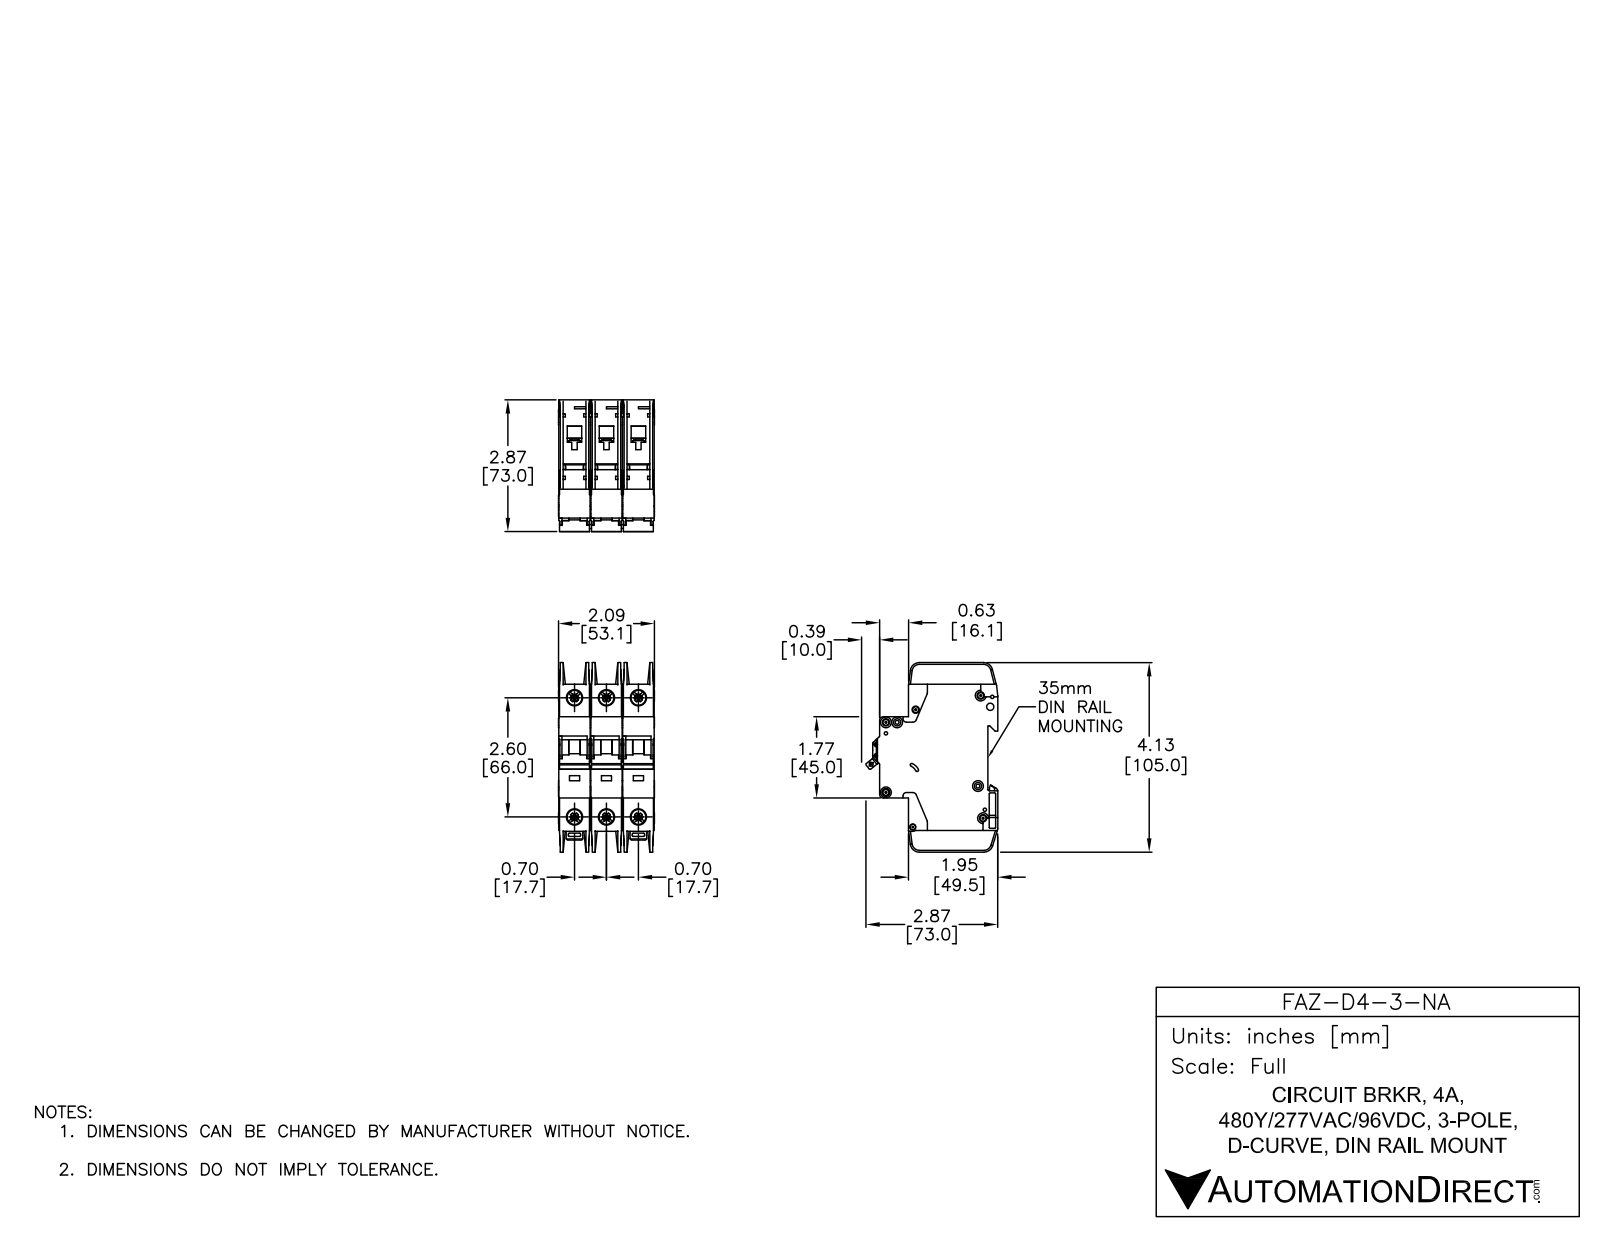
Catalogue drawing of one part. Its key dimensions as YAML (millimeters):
part_name: "FAZ-D4-3-NA"
step_written_by: "SolidWorks 2014 (AUTOMOTIVE_DESIGN)"
units: millimeters
bodies: {solids: 9, faces: 2352, planar: 1227, cylindrical: 789, other: 336}
overall_size: [105, 73.04, 53.1]
volume: 233085
surface_area: 74219
round_holes:
  - {diameter: 3.6, count: 7}
  - {diameter: 7.15, count: 6}
  - {diameter: 8.2, count: 6}
  - {diameter: 1.09, count: 2}
  - {diameter: 1.5, count: 2}
  - {diameter: 4, count: 2}
  - {diameter: 1.9, count: 1}
  - {diameter: 2.15, count: 1}
  - {diameter: 2.2, count: 1}
  - {diameter: 2.55, count: 1}
  - {diameter: 3.3, count: 1}
  - {diameter: 3.4, count: 1}
round_bosses_or_shafts:
  - {diameter: 6, count: 7}
  - {diameter: 2.5, count: 3}
partial_cylinders:
  - {radius: 0.25, count: 65}
  - {radius: 0.5, count: 30}
  - {radius: 1, count: 26}
  - {radius: 2, count: 14}
  - {radius: 1.8, count: 5}
  - {radius: 5, count: 5}
  - {radius: 4, count: 4}
  - {radius: 0.2, count: 2}
face_to_face_distances: [17.7, 35.4, 17.5, 35.2, 0.7, 15.05, 2.45, 1.75, 15.75, 13.3]
hole_center_spacings: [17.7, 68.33, 66, 6.2, 35.4, 74.89, 5.19, 6.1]
